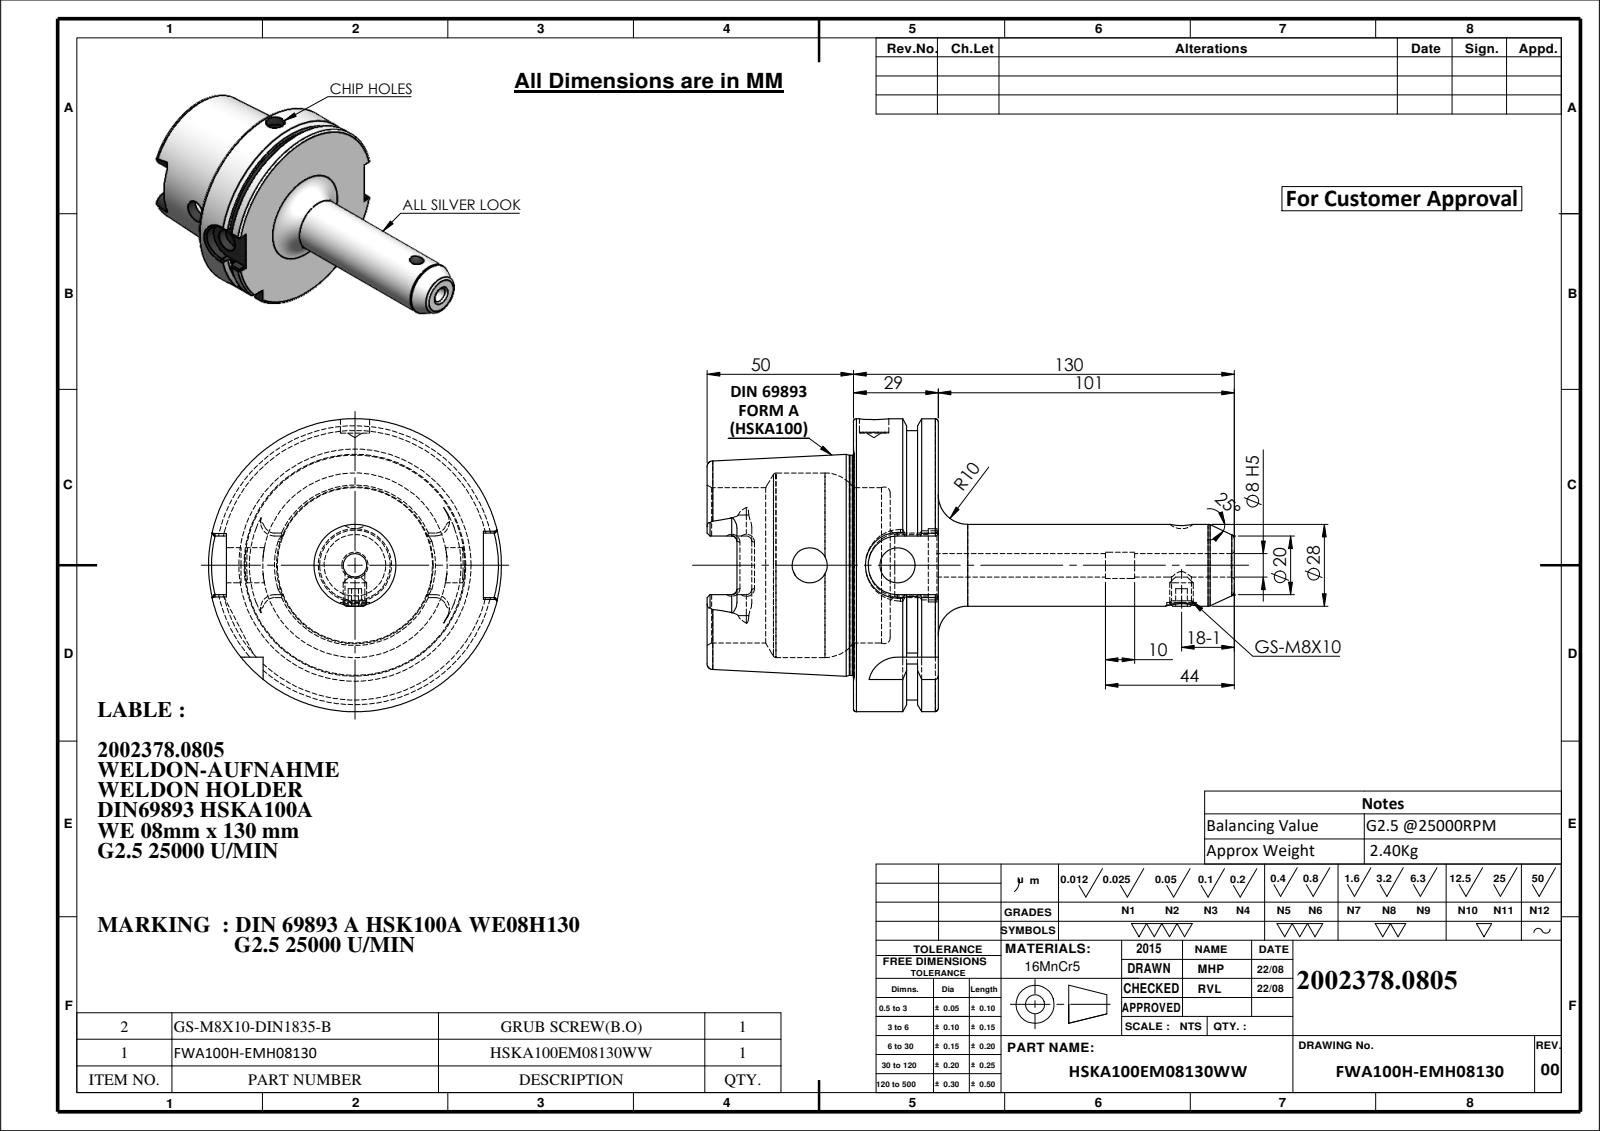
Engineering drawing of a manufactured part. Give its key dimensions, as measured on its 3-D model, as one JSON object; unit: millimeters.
{"part_name": "HSKA100EM08130WW; GS-M8X10-DIN1835-B; FWA100H-EMH08130", "step_written_by": "SolidWorks 2024 (CONFIG_CONTROL_DESIGN)", "units": "millimeters", "bodies": {"solids": 2, "faces": 203, "planar": 63, "cylindrical": 58, "other": 82}, "overall_size": [180, 100, 100], "volume_mm3": 311365, "surface_area_mm2": 61122, "round_holes": [[10, 2], [12, 2], [6.8, 1], [8, 1], [9, 1], [21, 1], [25, 1], [53, 1], [63, 1]], "round_bosses_or_shafts": [[100, 1], [92, 1], [75.16, 1], [28, 1], [8, 1]], "partial_cylinders_radius": [[1.8, 6], [4.88, 4], [10, 2], [11, 1]], "face_to_face_distances": [28.95, 12.5, 16.45, 50, 62.5, 78.95, 16, 78.5, 28.5, 0.45], "hole_center_spacings": [30, 105]}
